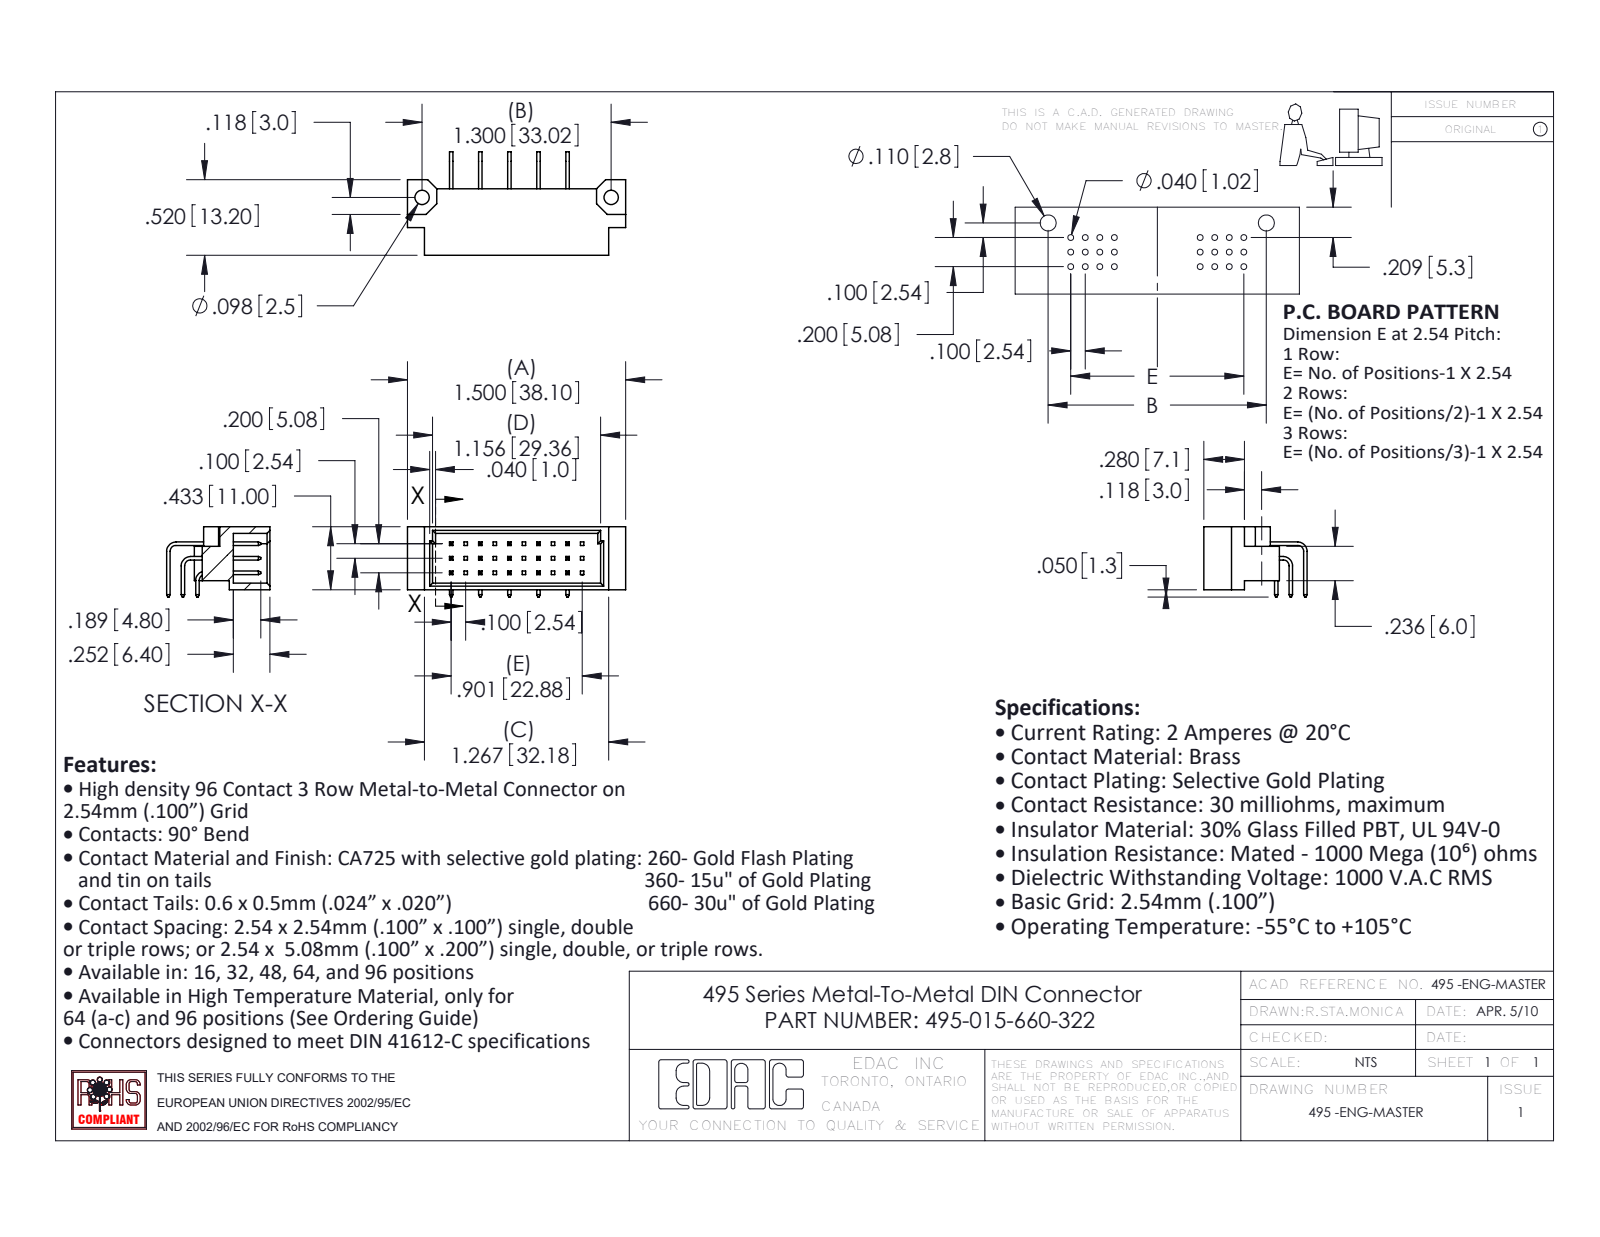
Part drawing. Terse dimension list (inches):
name: 495 Part_30; 495-290-3; 495-290-1; 495-290-2 (+1 more)
written by: SolidWorks 2020 (AUTOMOTIVE_DESIGN)
unit: in
bodies: 16 solids, 439 faces (405 planar, 34 cylindrical, 0 other)
size: 1.5 × 0.711 × 0.483
volume: 0.157 in³; area: 5.532 in²
holes: 2× ⌀0.098
rounds: 3× R0.04, 3× R0.065
face distances: 0.2, 0.388, 0.045, 0.1, 0.205, 0.4, 0.024, 0.433, 0.024, 0.063
hole spacings: 1.3
